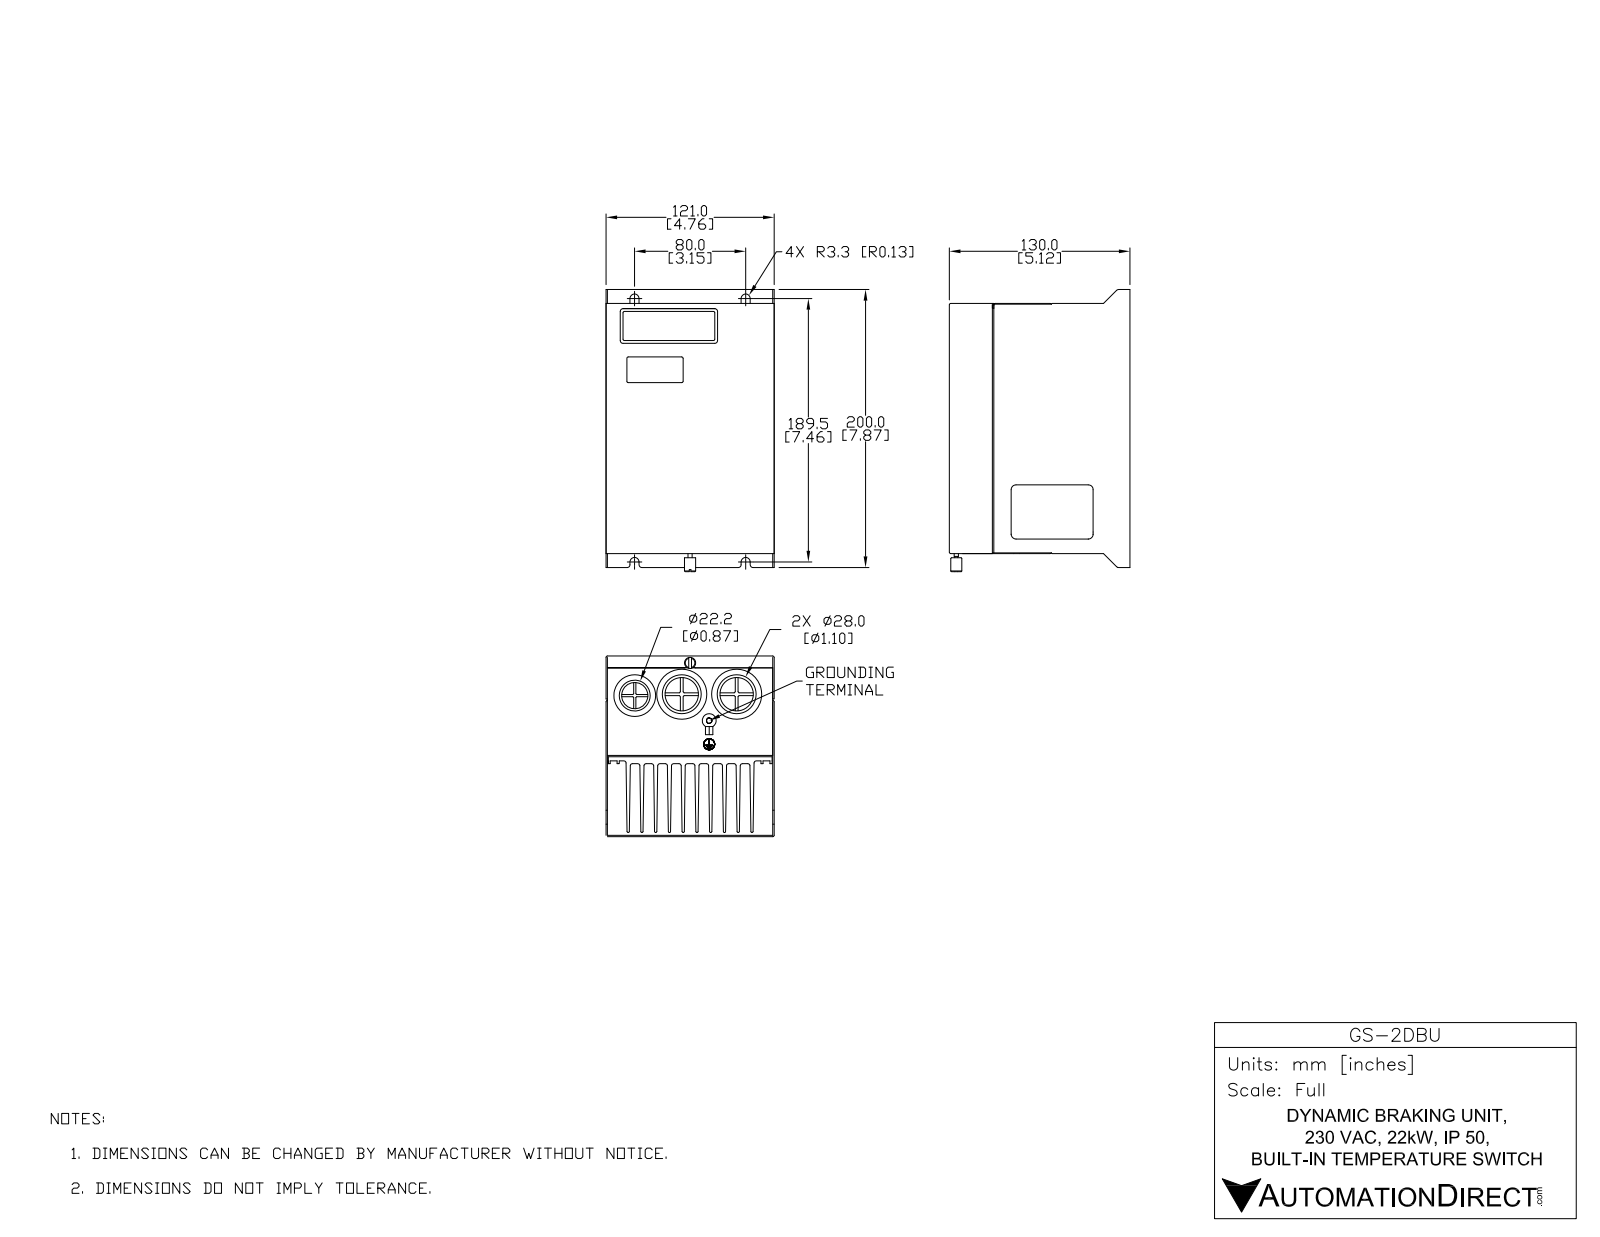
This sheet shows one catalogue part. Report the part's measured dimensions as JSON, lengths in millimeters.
{"part_name": "GS-2DBU", "step_written_by": "SolidWorks 2013 (AUTOMOTIVE_DESIGN)", "units": "millimeters", "bodies": {"solids": 1, "faces": 636, "planar": 389, "cylindrical": 111, "other": 136}, "overall_size": [201.8, 130.2, 120.9], "volume_mm3": 1904000, "surface_area_mm2": 290300, "round_holes": [[13.2, 2], [25.4, 2], [17.8, 1]], "round_bosses_or_shafts": [[38.1, 2], [28.6, 1], [9.5, 1], [5.4, 1], [3.2, 1]], "partial_cylinders_radius": [[1.5, 38], [0.8, 20], [0.5, 4], [2.5, 4], [3.3, 4], [5, 2], [2, 1], [2.7, 1]], "face_to_face_distances": [20.8, 31.2, 10.4, 52.1, 1.6, 10.4, 41.7, 120.9, 72.9, 41.7], "hole_center_spacings": [38, 39.4, 77.4, 80]}
